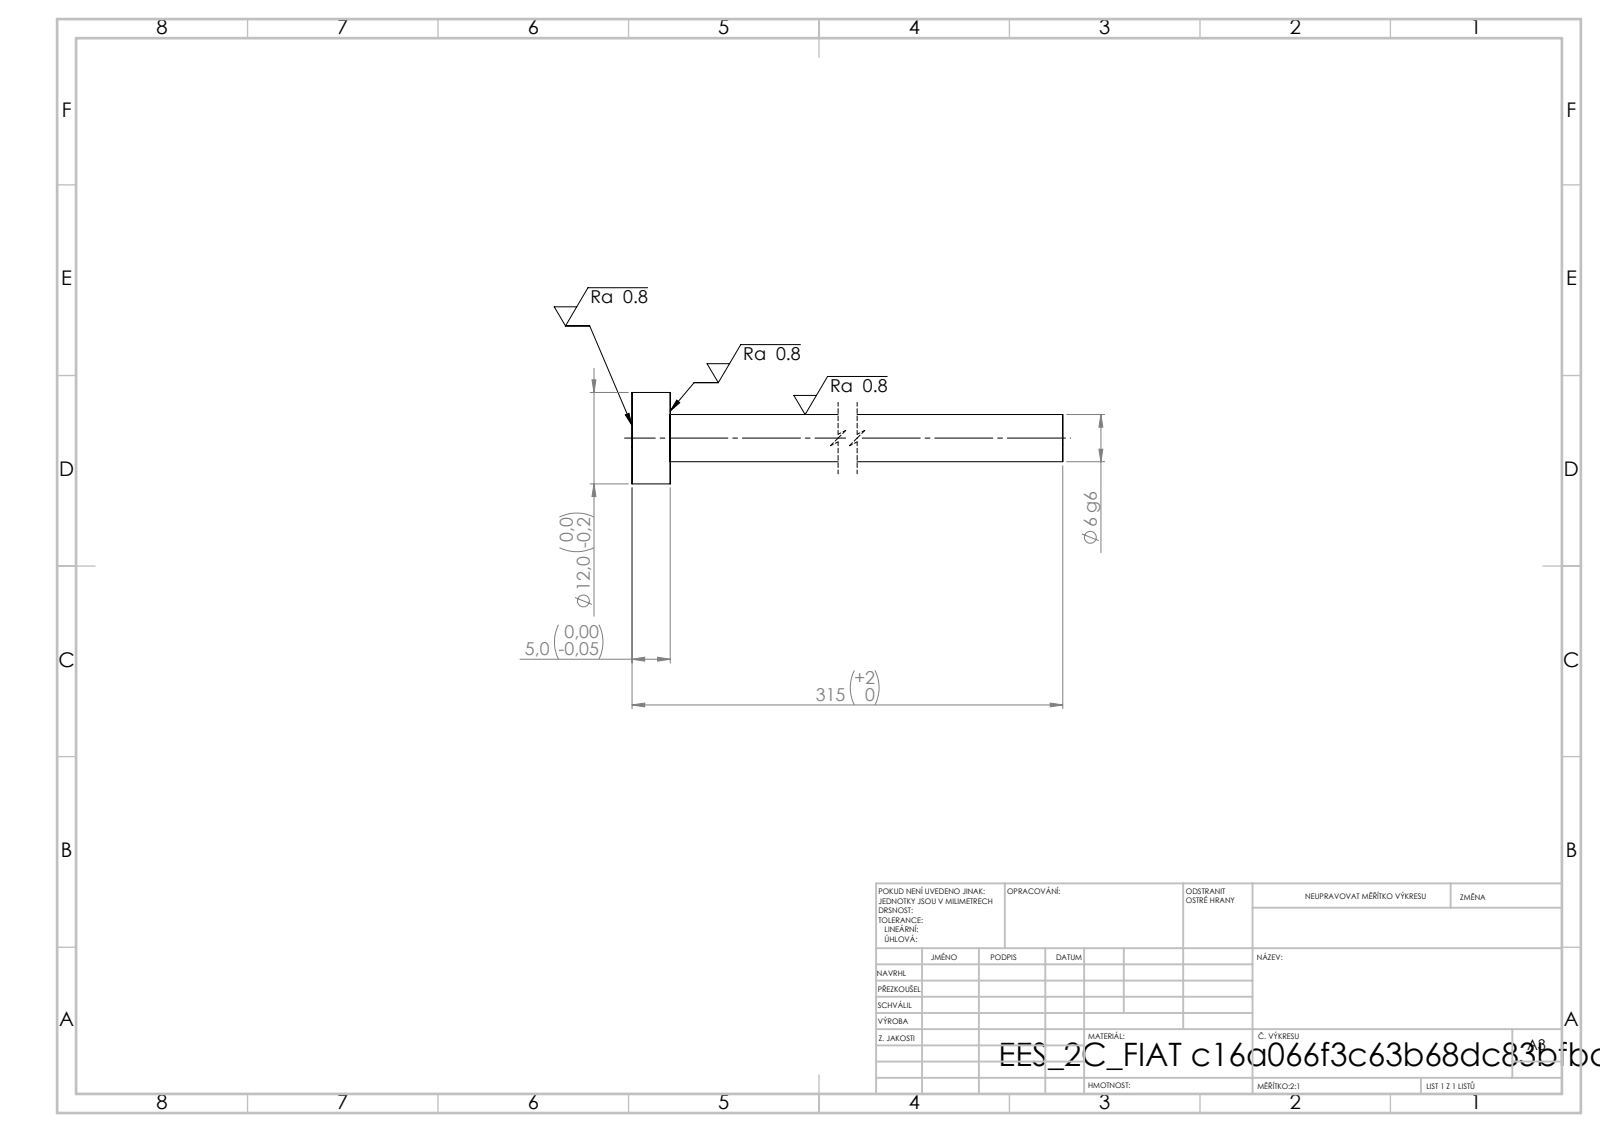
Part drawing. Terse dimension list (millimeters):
written by: SolidWorks 2019 (CONFIG_CONTROL_DESIGN)
unit: mm
bodies: 1 solid, 7 faces (3 planar, 4 cylindrical, 0 other)
size: 315 × 12 × 12
volume: 9 925 mm³; area: 6 453 mm²
bosses: 1× ⌀12, 1× ⌀6.2
face distances: 5, 315, 310
